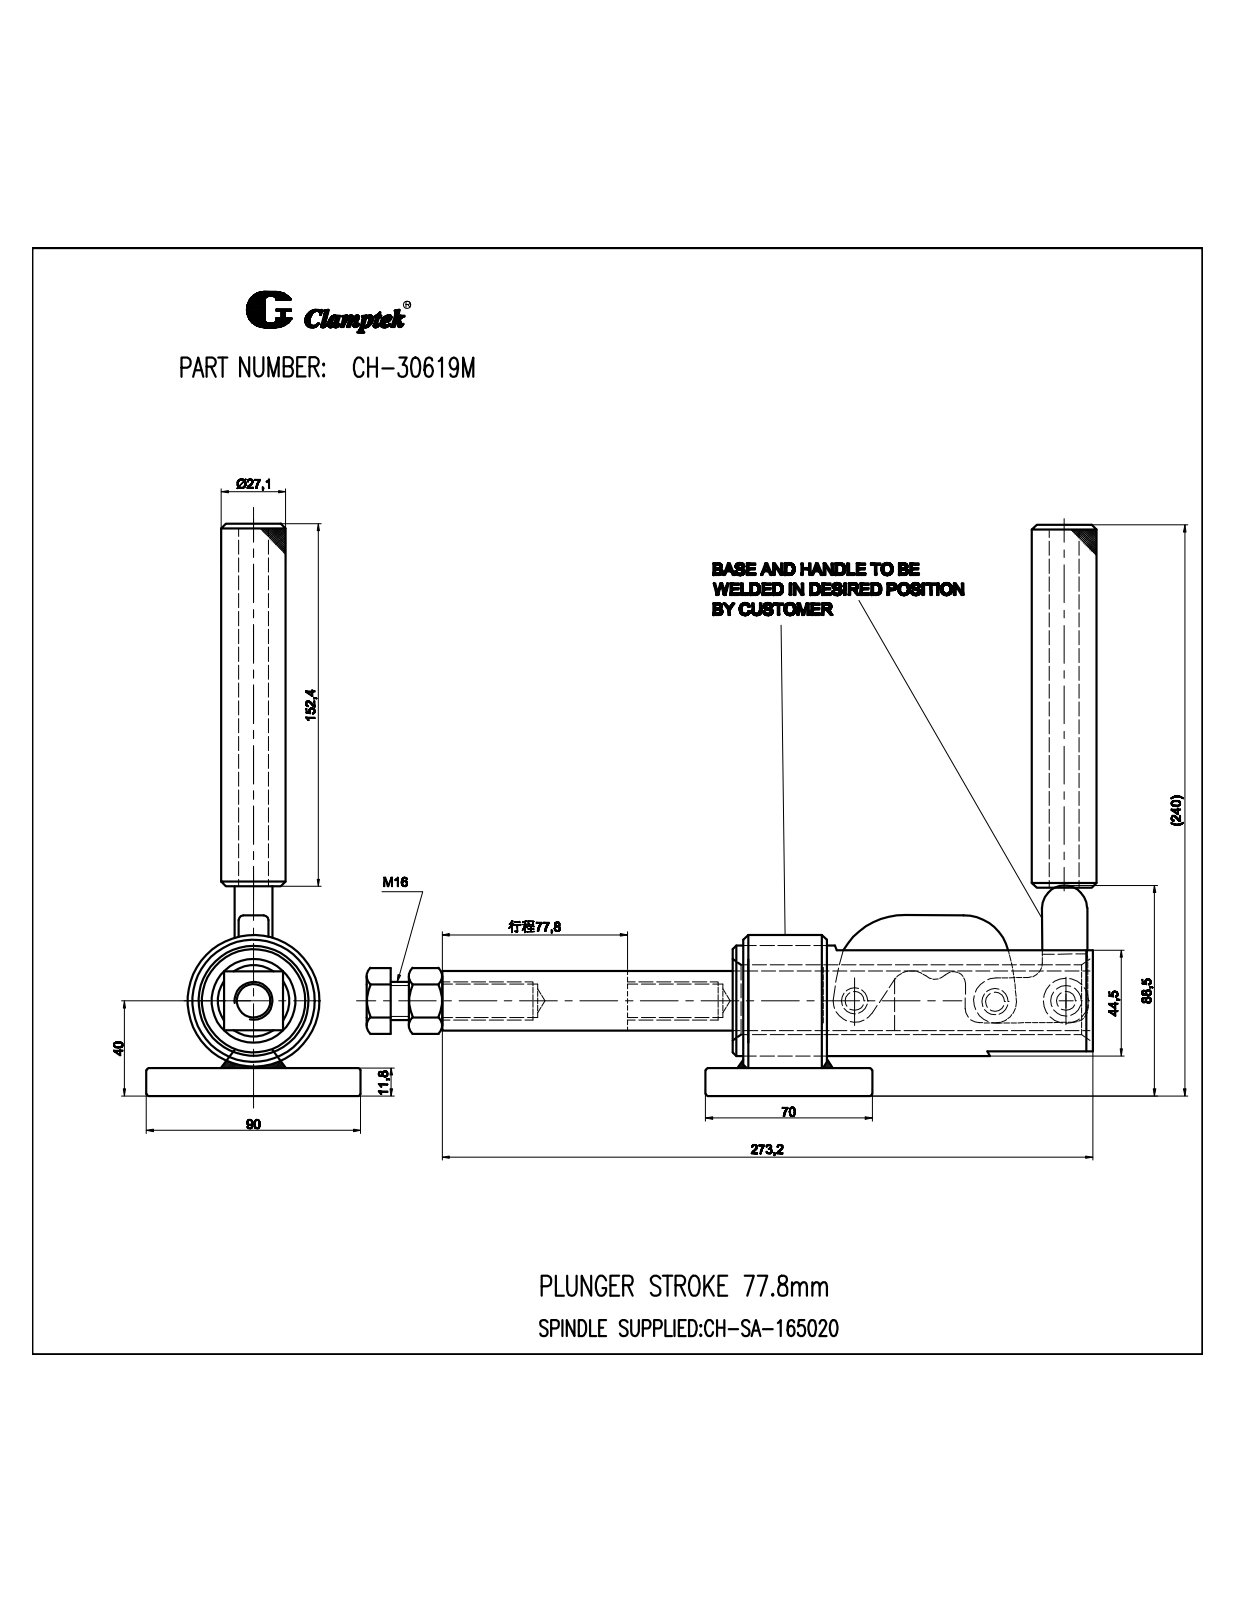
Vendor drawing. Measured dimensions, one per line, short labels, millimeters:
name: CH-30619M; M16螺栓_默认
written by: SolidWorks 2008 (CONFIG_CONTROL_DESIGN)
unit: mm
bodies: 19 solids, 726 faces (281 planar, 176 cylindrical, 269 other)
size: 297.4 × 237.85 × 90
volume: 476 781 mm³; area: 166 912 mm²
holes: 3× ⌀9.5, 2× ⌀12.8, 2× ⌀14, 1× ⌀3.09, 1× ⌀14.2, 1× ⌀21.7, 1× ⌀45
bosses: 1× ⌀57, 1× ⌀27.2, 1× ⌀25, 1× ⌀16, 1× ⌀2.72
rounds: 4× R12.5, 2× R12, 2× R70, 1× R12.4, 1× R13.5, 1× R14.5, 1× R29.3
face distances: 18.5, 6.5, 25, 11.5, 12, 16, 27.5, 0.5, 41, 6
hole spacings: 36.46, 39.1, 63.81, 77, 99.9, 116.1
